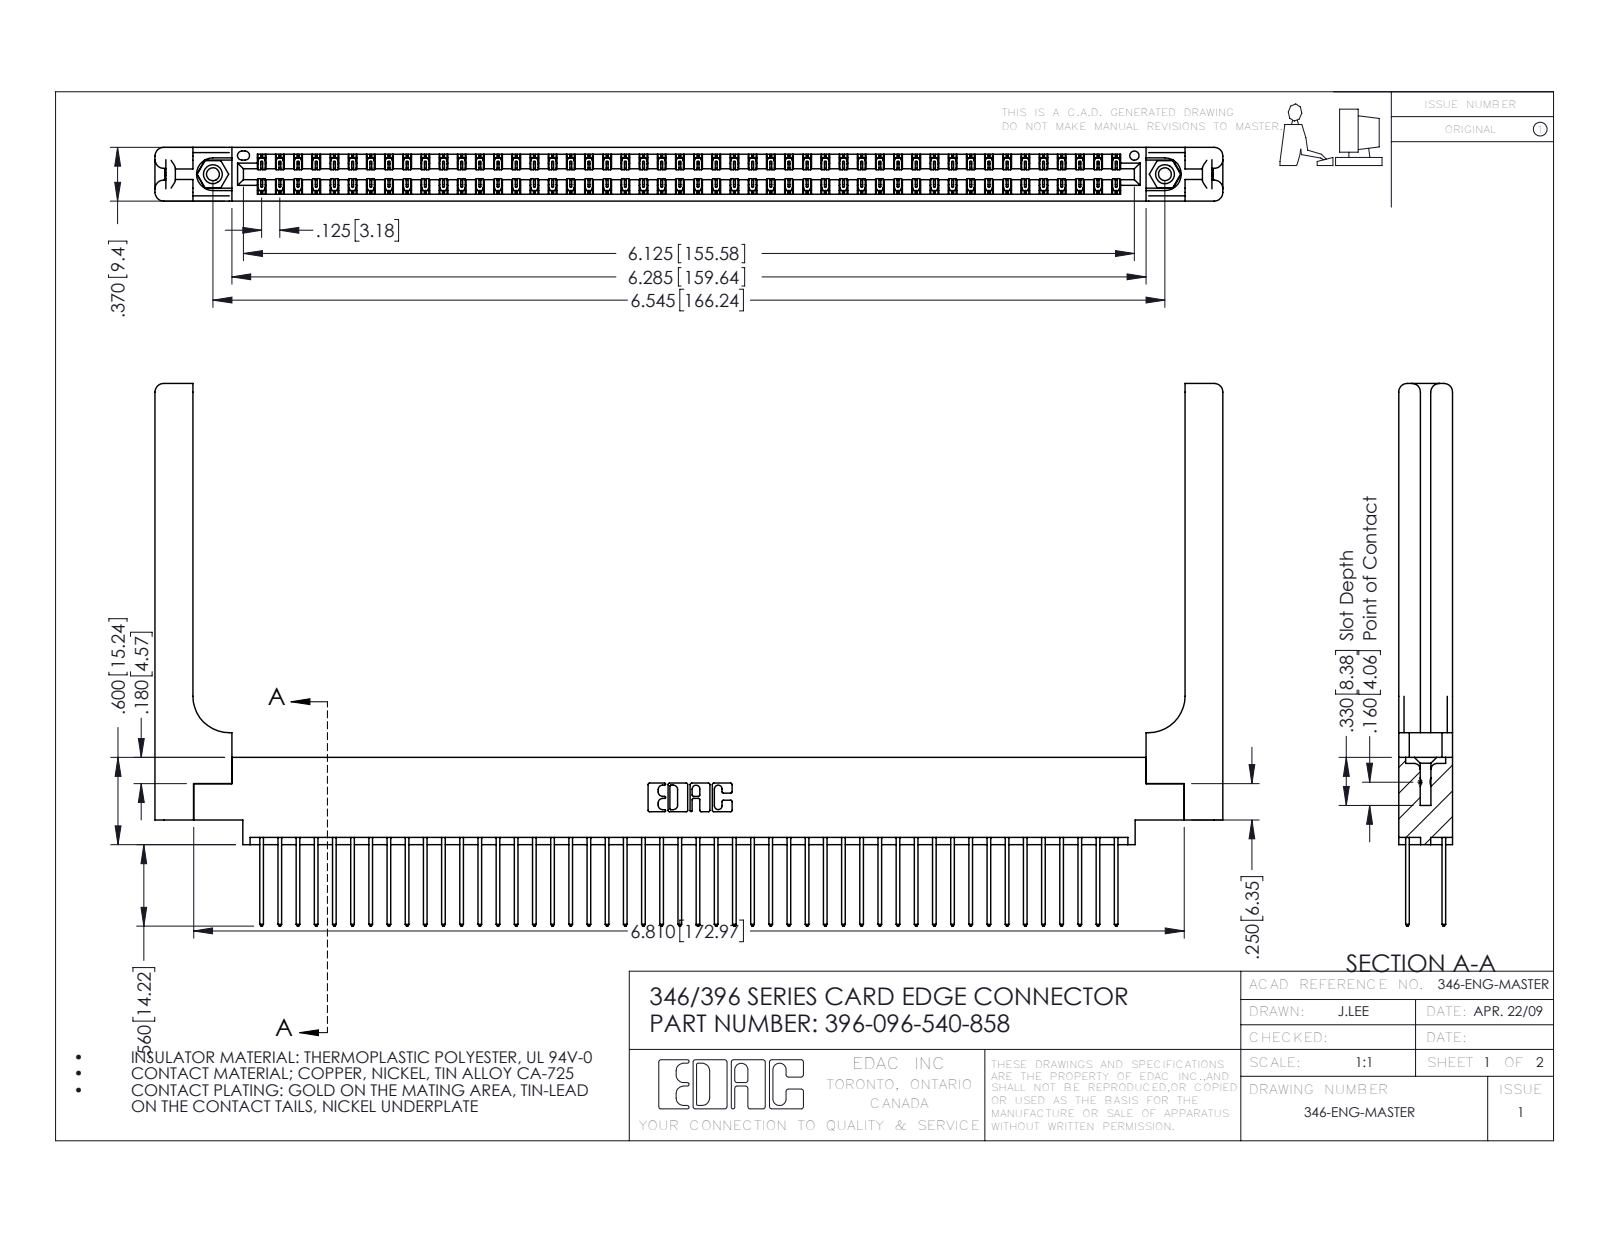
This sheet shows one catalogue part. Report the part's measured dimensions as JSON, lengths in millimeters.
{"part_name": "346 Part_0.170 Offset - 0.156 Dia-TH; 396-096-540-858; 346-220-058_345-220-058; 345-250-001_345-250-001-102 (+1 more)", "step_written_by": "SolidWorks 2016 (CONFIG_CONTROL_DESIGN)", "units": "millimeters", "bodies": {"solids": 101, "faces": 5374, "planar": 3588, "cylindrical": 1726, "other": 60}, "overall_size": [186.5, 94.7, 9.4], "volume_mm3": 25920, "surface_area_mm2": 32310, "round_holes": [[2.3, 2], [3.2, 2], [4, 2], [1.6, 1]], "round_bosses_or_shafts": [[3.9, 2]], "partial_cylinders_radius": [[0.2, 144], [0.3, 96], [0.3, 22], [1.5, 16], [0.2, 6], [0.8, 6], [0.7, 3], [0.4, 2]], "face_to_face_distances": [1.2, 8.2, 9.4, 1.8, 6.4, 0.6, 7.6, 3.8, 3.8, 7], "hole_center_spacings": [6.2, 160.9, 166.2]}
